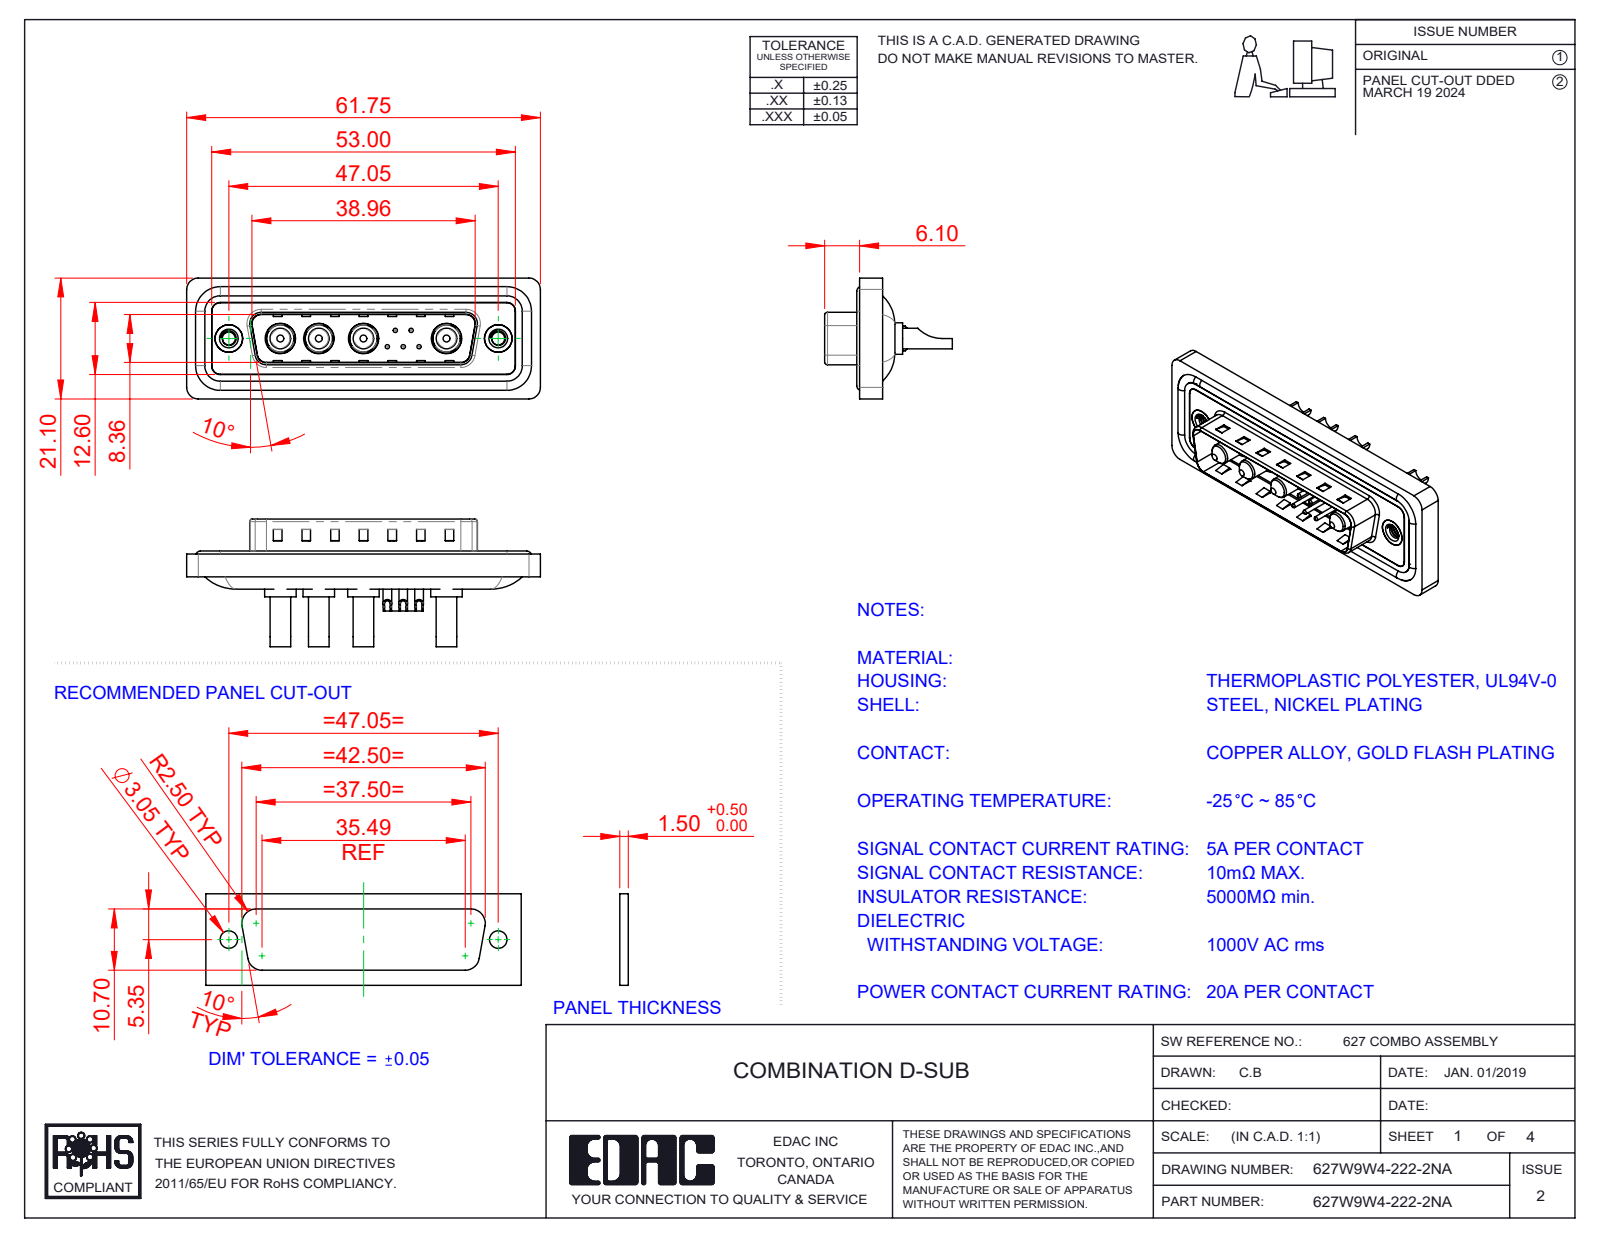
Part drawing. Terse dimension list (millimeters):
name: 627Combo Housing_9W4; 627Combo Shell Front_25 Contacts; 627Combo Threaded Rivet_A; 627Combo Contact Row 2_22 (+5 more)
written by: SolidWorks 2023 (CONFIG_CONTROL_DESIGN)
unit: mm
bodies: 20 solids, 850 faces (306 planar, 358 cylindrical, 186 other)
size: 61.75 × 22.3 × 21.1
volume: 7 465 mm³; area: 12 203 mm²
holes: 5× ⌀0.75, 5× ⌀1, 5× ⌀1.6, 5× ⌀2, 4× ⌀2.7, 4× ⌀4.85, 4× ⌀5.3, 2× ⌀2.26, 2× ⌀4, 2× ⌀4.8, 2× ⌀5
bosses: 5× ⌀1.5, 4× ⌀5.5, 4× ⌀5.2, 4× ⌀4.75, 4× ⌀3.75, 4× ⌀3.6, 4× ⌀1.6, 2× ⌀4.9
rounds: 22× R1.5, 18× R2, 8× R0.5, 8× R1.6, 6× R1, 4× R0.25, 4× R0.6, 4× R0.65
face distances: 0.4, 1.5, 1.1, 0.5, 1.6, 3.1, 2.9, 0.82, 9.58, 5.65
hole spacings: 3.16, 2.77, 5.04, 14.51, 2.78, 4.4, 4.41, 5
